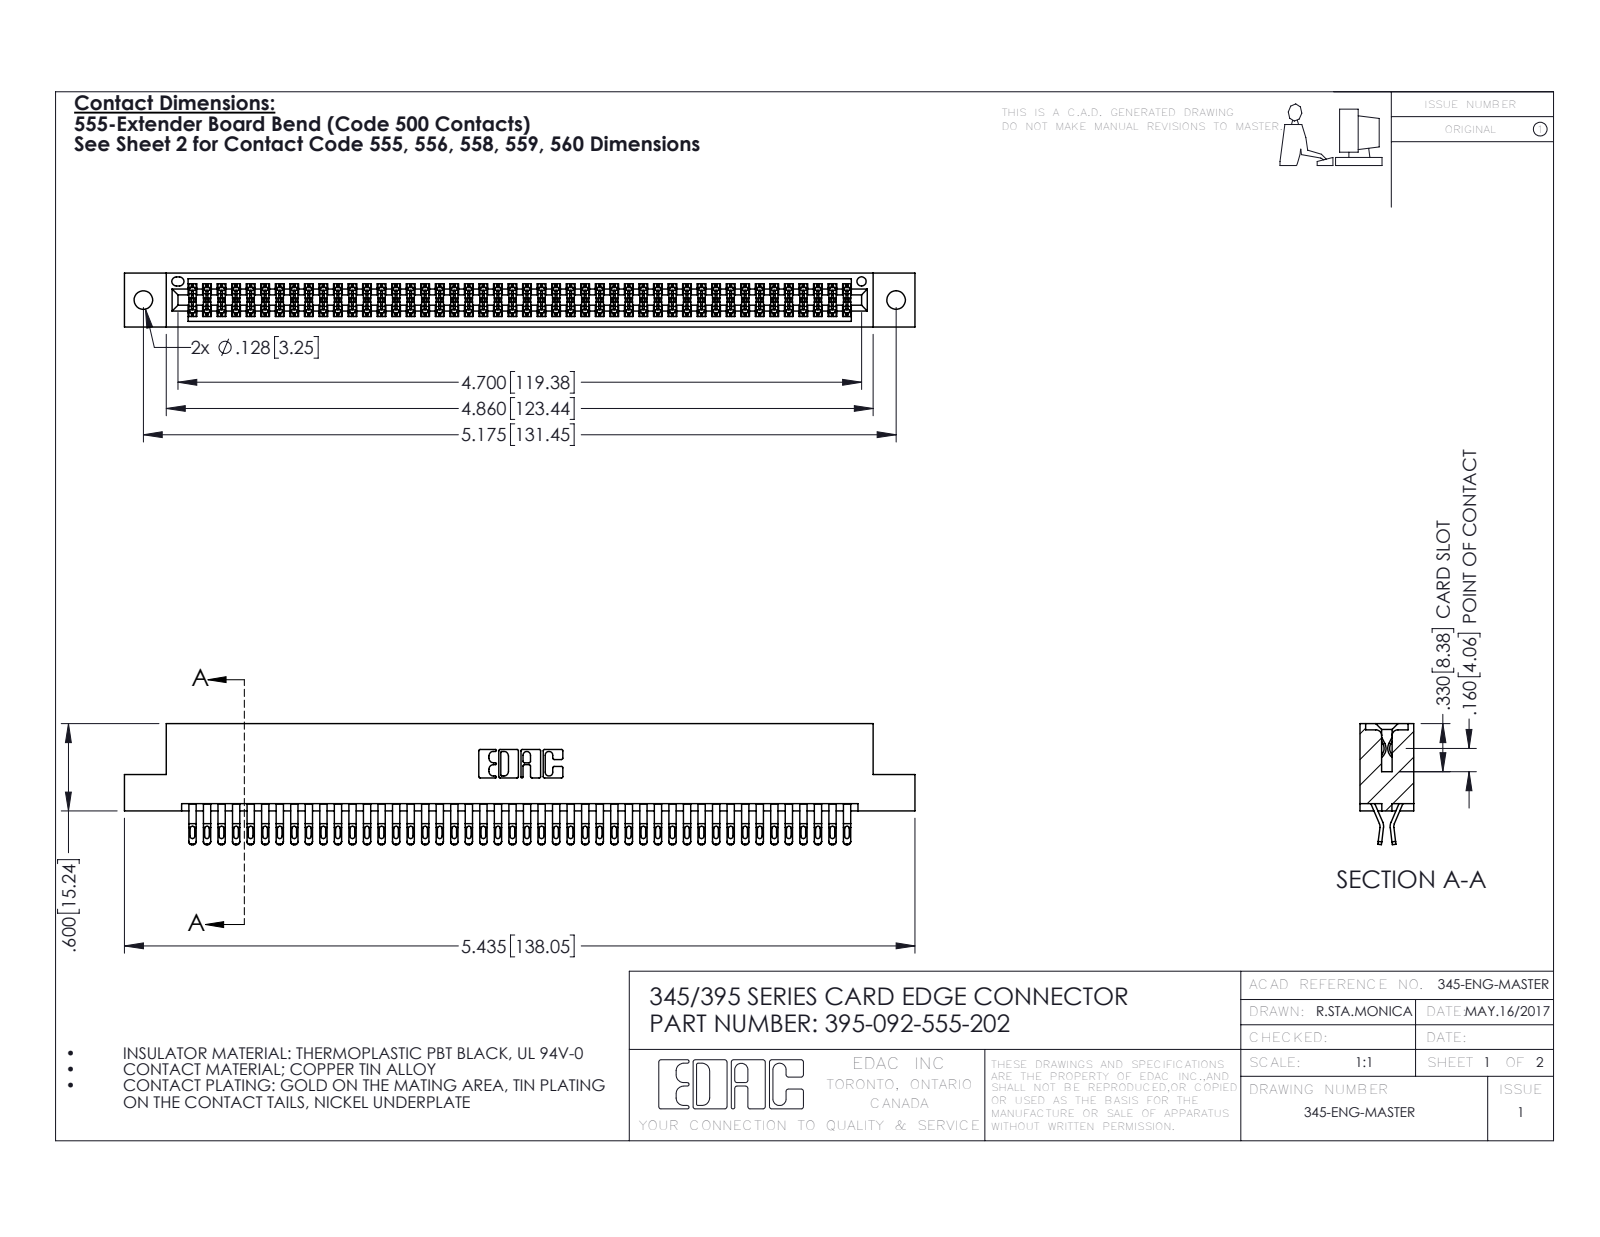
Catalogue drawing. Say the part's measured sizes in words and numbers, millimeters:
The part is named "345 Part_Flush Mounting Lugs - 0.128 Dia; 345-292-001_555 Tail; 395-092-555-202". Its 3-D file was written by "SolidWorks 2016 (CONFIG_CONTROL_DESIGN)". It is 93 solids with 5278 faces: 2932 planar, 2346 cylindrical and 0 other. Overall it measures 138 by 21.1 by 9.4 millimeters. Its volume is 13 700 cubic millimeters and its surface area 20 950 square millimeters. Round holes: 2 of diameter 3.3, 1 of diameter 1.6. Partial cylindrical surfaces (rounded edges, fillets, slot ends): 230 of radius 0.4, 184 of radius 0.5, 138 of radius 0.2, 22 of radius 0.3, 6 of radius 0.2, 6 of radius 0.8, 3 of radius 0.7, 2 of radius 0.3. The main face-to-face distances are 7.6, 1.8, 0.6, 9.4, 5.1, 2.5, 6.9, 5.7, 4.4, 3.8. The hole center spacings are 6.9, 125.5, 131.4.
